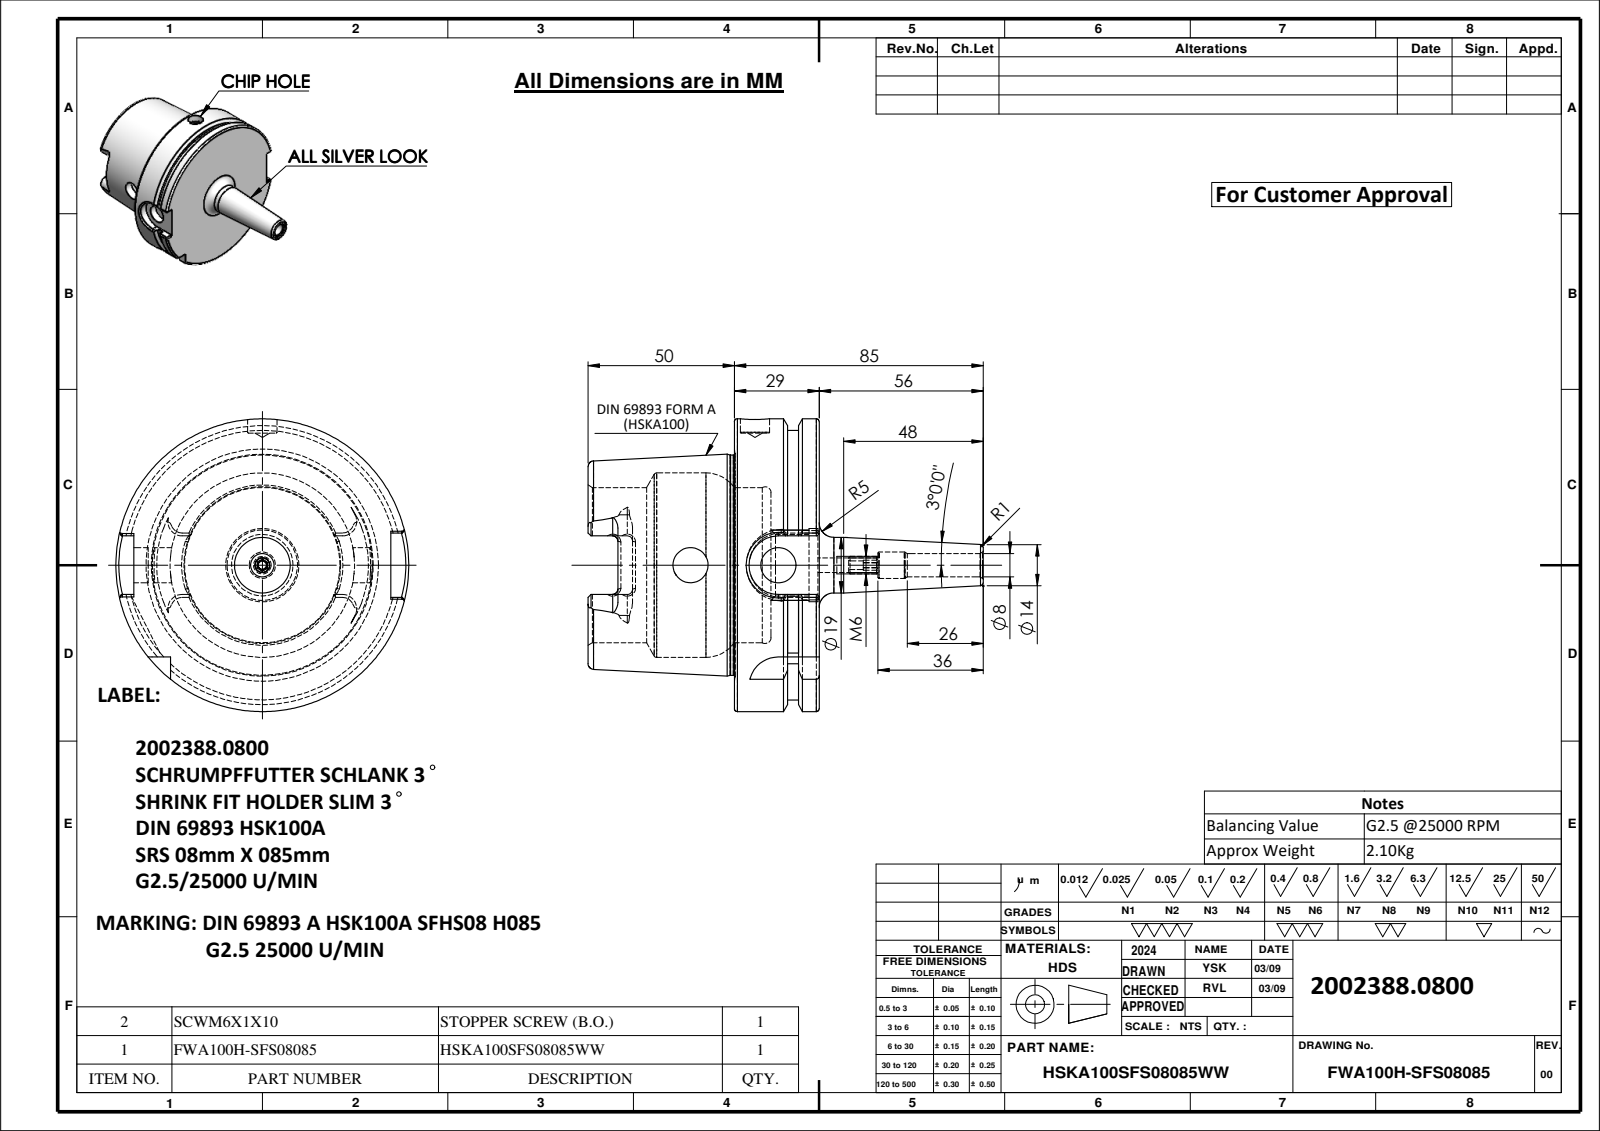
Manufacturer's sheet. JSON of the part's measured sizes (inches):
{"part_name": "FWA100H-SFS08085; SCWM6-10; HSKA100SFS08085WW", "step_written_by": "SolidWorks 2024 (CONFIG_CONTROL_DESIGN)", "units": "inches", "bodies": {"solids": 2, "faces": 207, "planar": 67, "cylindrical": 56, "other": 84}, "overall_size": [5.315, 3.937, 3.937], "volume_in3": 16.14, "surface_area_in2": 83.91, "round_holes": [[0.472, 2], [0.114, 1], [0.197, 1], [0.315, 1], [0.354, 1], [0.394, 1], [0.827, 1], [0.984, 1], [2.087, 1], [2.48, 1]], "round_bosses_or_shafts": [[3.937, 1], [3.622, 1], [2.959, 1], [0.748, 1], [0.236, 1]], "partial_cylinders_radius": [[0.071, 6], [0.192, 4], [0.394, 2], [0.433, 1]], "face_to_face_distances": [1.14, 0.492, 0.648, 1.969, 2.461, 3.108, 3.091, 1.122, 0.63, 0.018], "hole_center_spacings": [1.181]}
